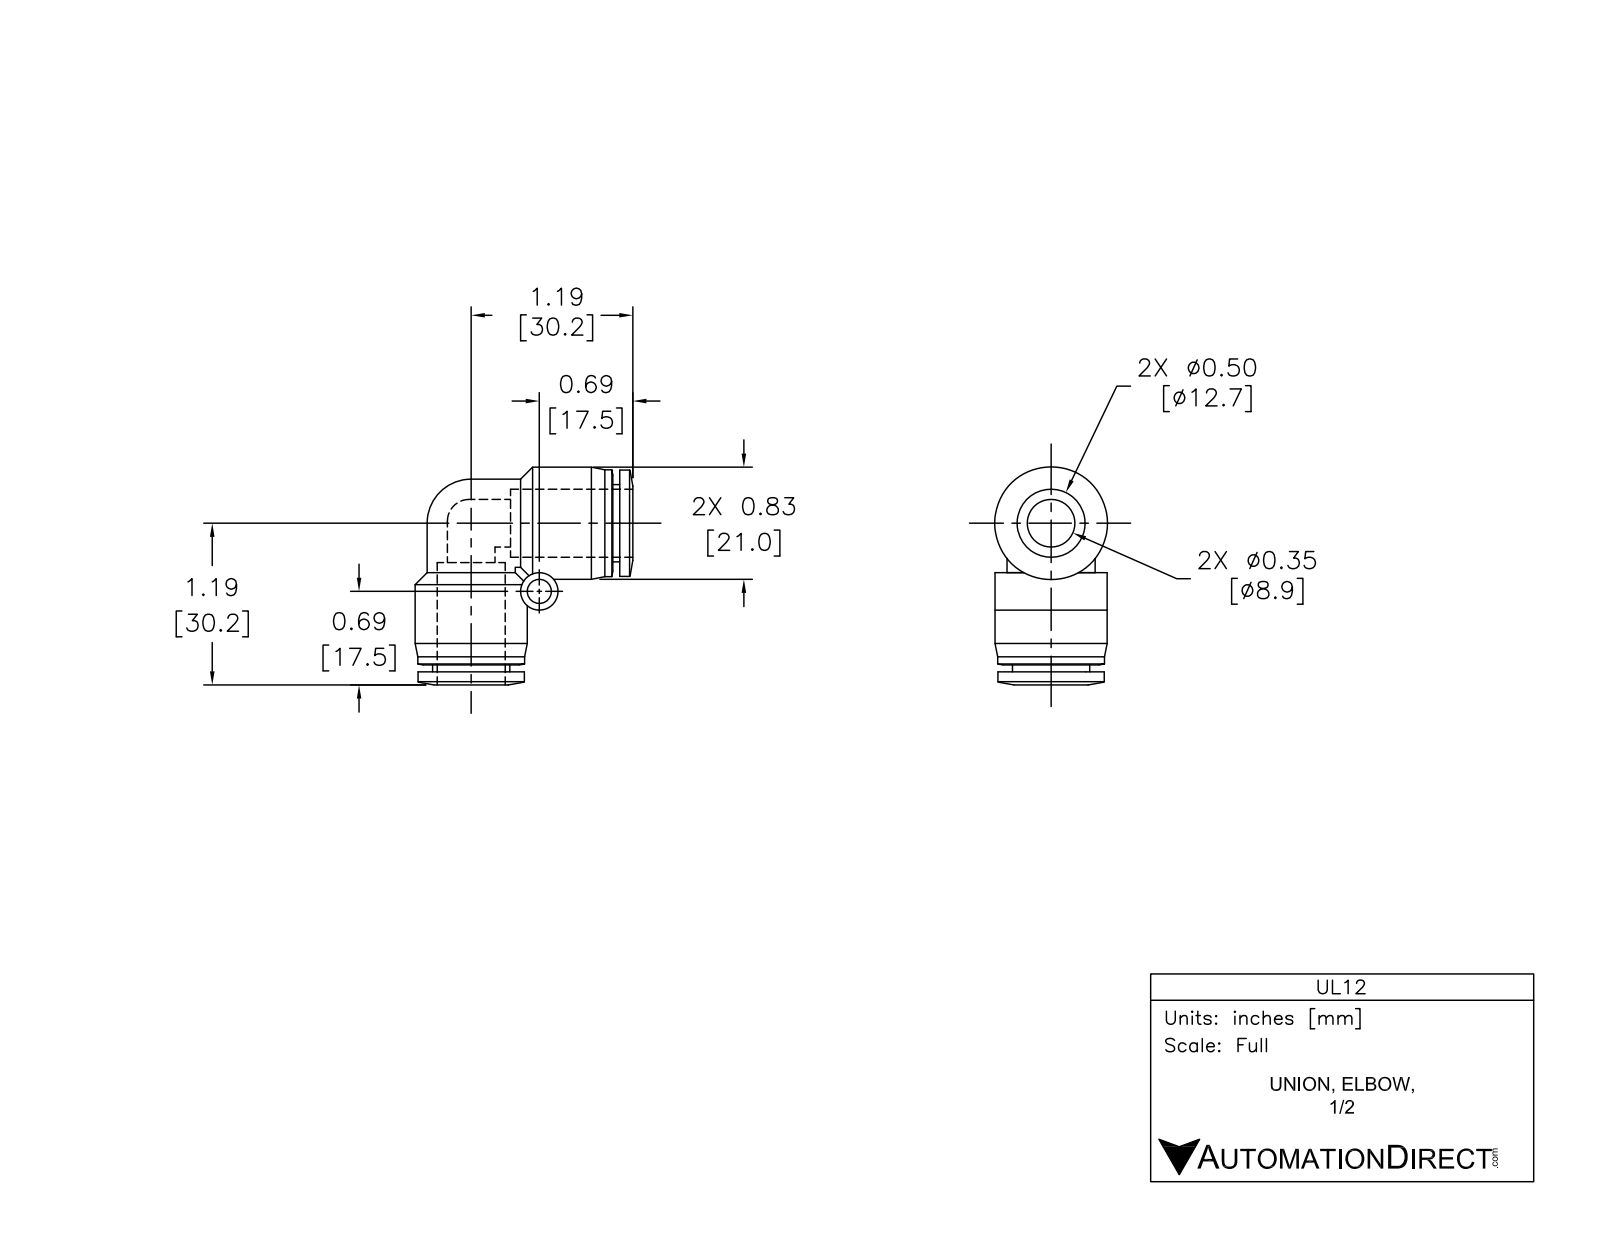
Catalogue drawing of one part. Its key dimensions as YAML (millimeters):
part_name: "UL12"
step_written_by: "SolidWorks 2015 (AUTOMOTIVE_DESIGN)"
units: millimeters
bodies: {solids: 1, faces: 72, planar: 8, cylindrical: 32, other: 32}
overall_size: [40.7, 40.7, 21]
volume: 10400
surface_area: 7568
round_holes:
  - {diameter: 10, count: 2}
  - {diameter: 13, count: 2}
  - {diameter: 4.5, count: 1}
round_bosses_or_shafts:
  - {diameter: 21, count: 2}
  - {diameter: 20, count: 2}
  - {diameter: 19.9, count: 2}
  - {diameter: 16.5, count: 2}
  - {diameter: 14.5, count: 2}
  - {diameter: 7, count: 1}
face_to_face_distances: [1.3, 19.4, 20.7, 21]
